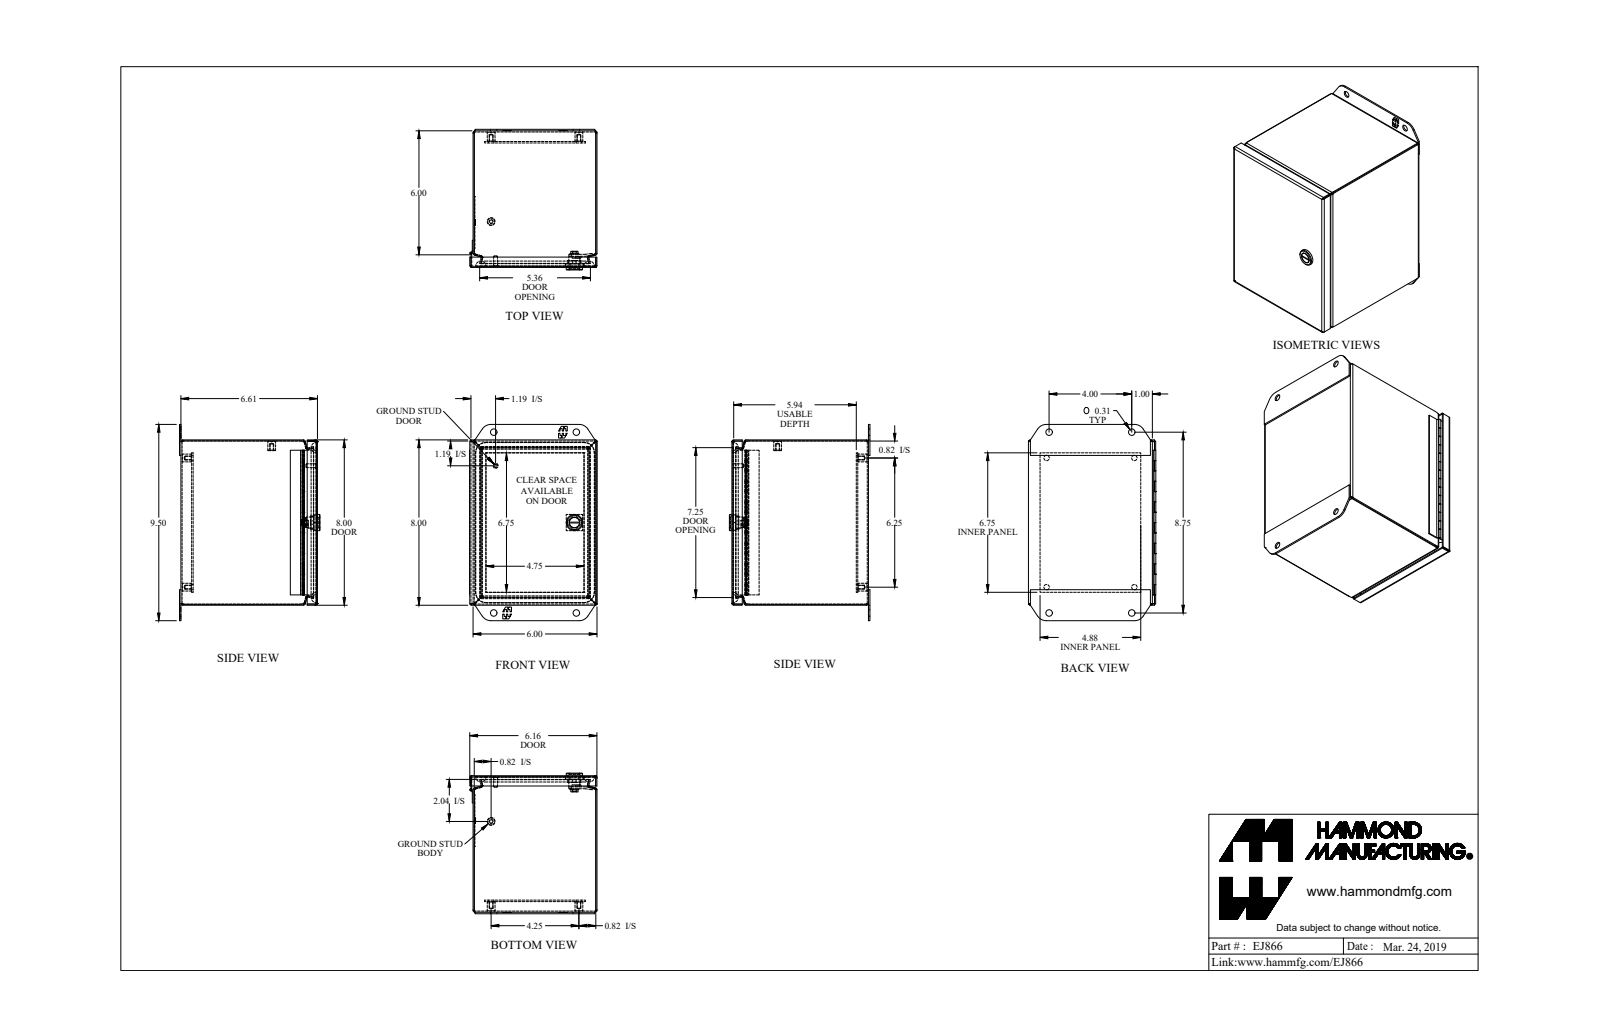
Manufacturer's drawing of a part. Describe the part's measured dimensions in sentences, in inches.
The part is named "EJ866_Default". Its 3-D file was written by "SolidWorks 2019 (CONFIG_CONTROL_DESIGN)". It is 16 solids with 643 faces: 361 planar, 190 cylindrical and 92 other. Overall it measures 9.5 by 6.805 by 6.165 inches. Its volume is 23.3 cubic inches and its surface area 775.7 square inches. Round holes: 5 of diameter 0.156, 4 of diameter 0.265, 4 of diameter 0.313, 1 of diameter 0.05, 1 of diameter 0.516. Round bosses or shafts: 5 of diameter 0.375, 1 of diameter 0.788, 1 of diameter 0.535, 1 of diameter 0.496, 1 of diameter 0.435, 1 of diameter 0.25, 1 of diameter 0.188, 1 of diameter 0.1. Partial cylindrical surfaces (rounded edges, fillets, slot ends): 16 of radius 0.029, 16 of radius 0.086, 10 of radius 0.281, 4 of radius 0.25, 4 of radius 0.499, 4 of radius 0.5, 2 of radius 0.06, 2 of radius 0.539. The main face-to-face distances are 0.057, 6.554, 5.943, 7.943, 0.072, 0.589, 5.886, 6.611, 6, 6.497. The hole center spacings are 1.256, 4.31, 7.502, 8.56, 3.133, 4, 4.25, 4.376.
